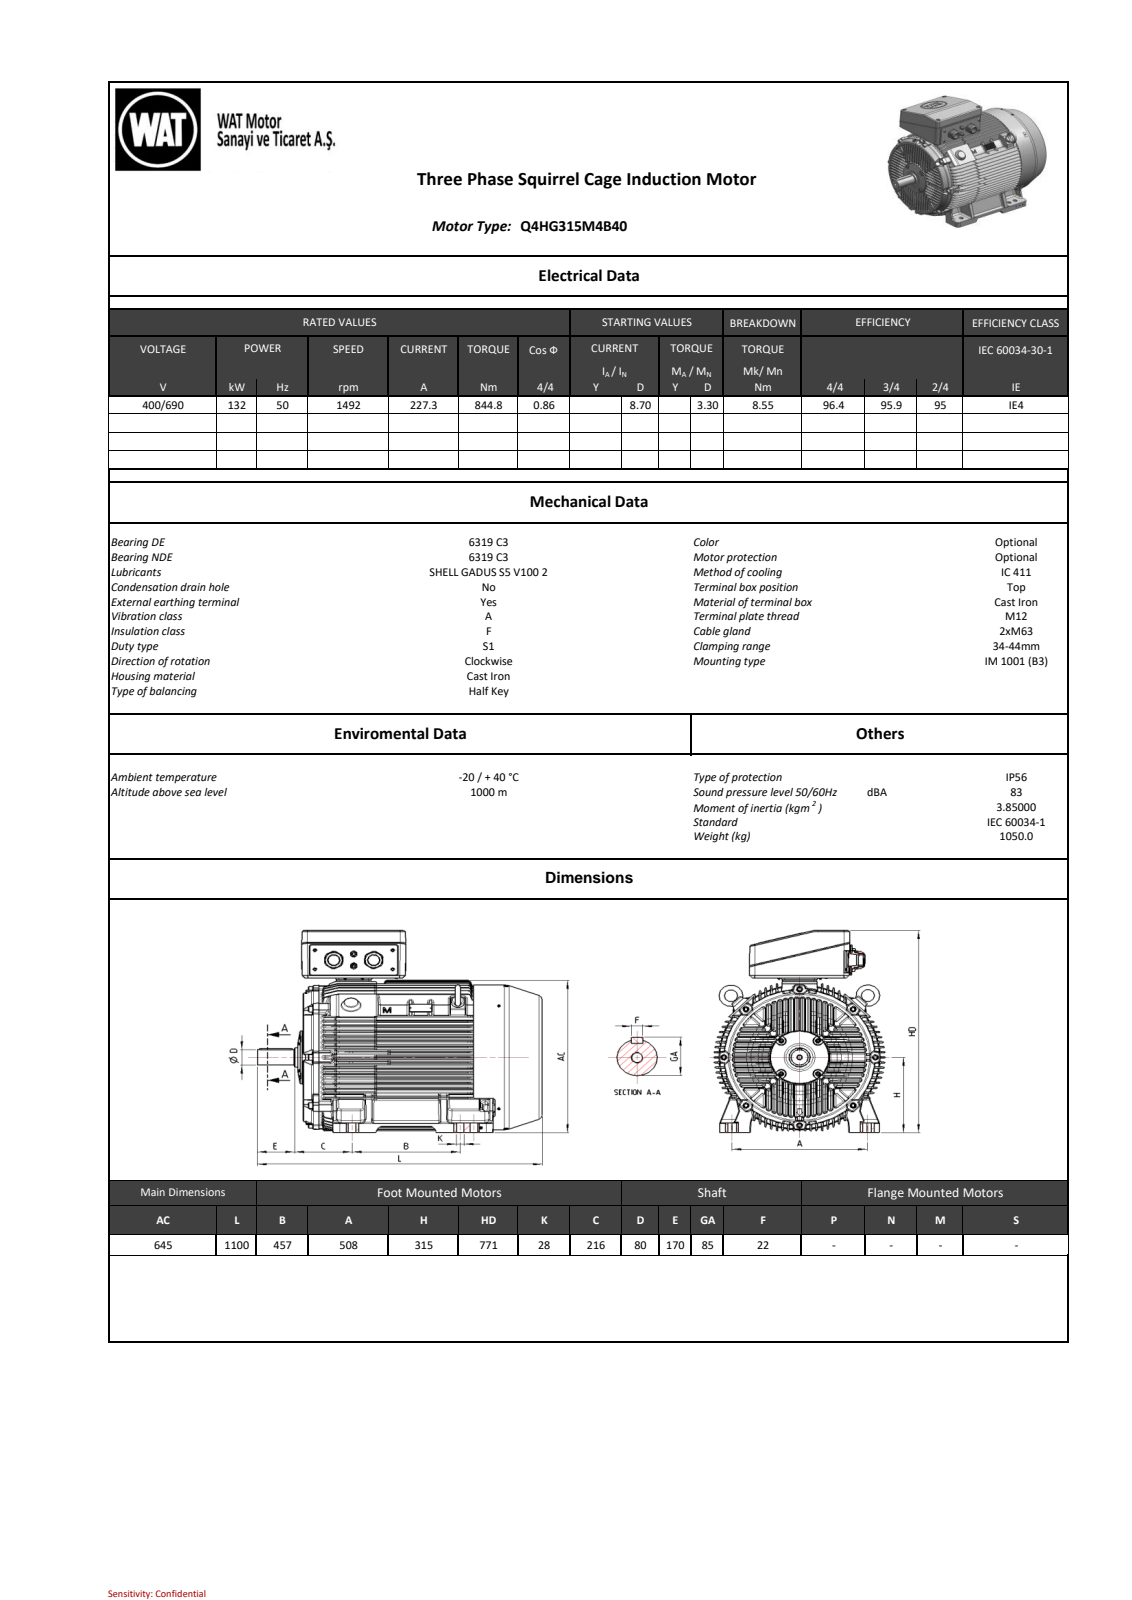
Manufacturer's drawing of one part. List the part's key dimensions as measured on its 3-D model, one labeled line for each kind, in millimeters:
Part name (STEP PRODUCT): 26009910674F4pxy
STEP written by: SIEMENS PLM Software NX 11.0 (AUTOMOTIVE_DESIGN)
Units: millimetres
Bodies: 0 solids, 8844 faces (3557 planar, 1827 cylindrical, 3460 other)
Overall size (bounding box): 1100 × 847.37 × 645
Round holes (diameter × count): ⌀20 ×8, ⌀5 ×4, ⌀4 ×2, ⌀8.5 ×2, ⌀8.8 ×2, ⌀9 ×2, ⌀12 ×2, ⌀44 ×2, ⌀44.4 ×2, ⌀44.5 ×2, ⌀47.7 ×2, ⌀8 ×1
Round bosses / shafts (diameter × count): ⌀24 ×8, ⌀16 ×8, ⌀20 ×4, ⌀10 ×4, ⌀64.8 ×2, ⌀50 ×2, ⌀607 ×1, ⌀565 ×1
Partial cylindrical surfaces — rounded edges, fillets, slot ends (radius × count): R6 ×726, R3 ×197, R1.5 ×152, R2.09 ×59, R2.61 ×54, R0.8 ×37, R15 ×34, R10 ×26
Main face-to-face distances: 117, 20.8, 263.64, 20.71, 305.15, 242.75, 221.95, 41.69, 20.89, 284.35
Hole centre spacings: 150, 79.05, 79.06, 739, 0.33, 30, 50
